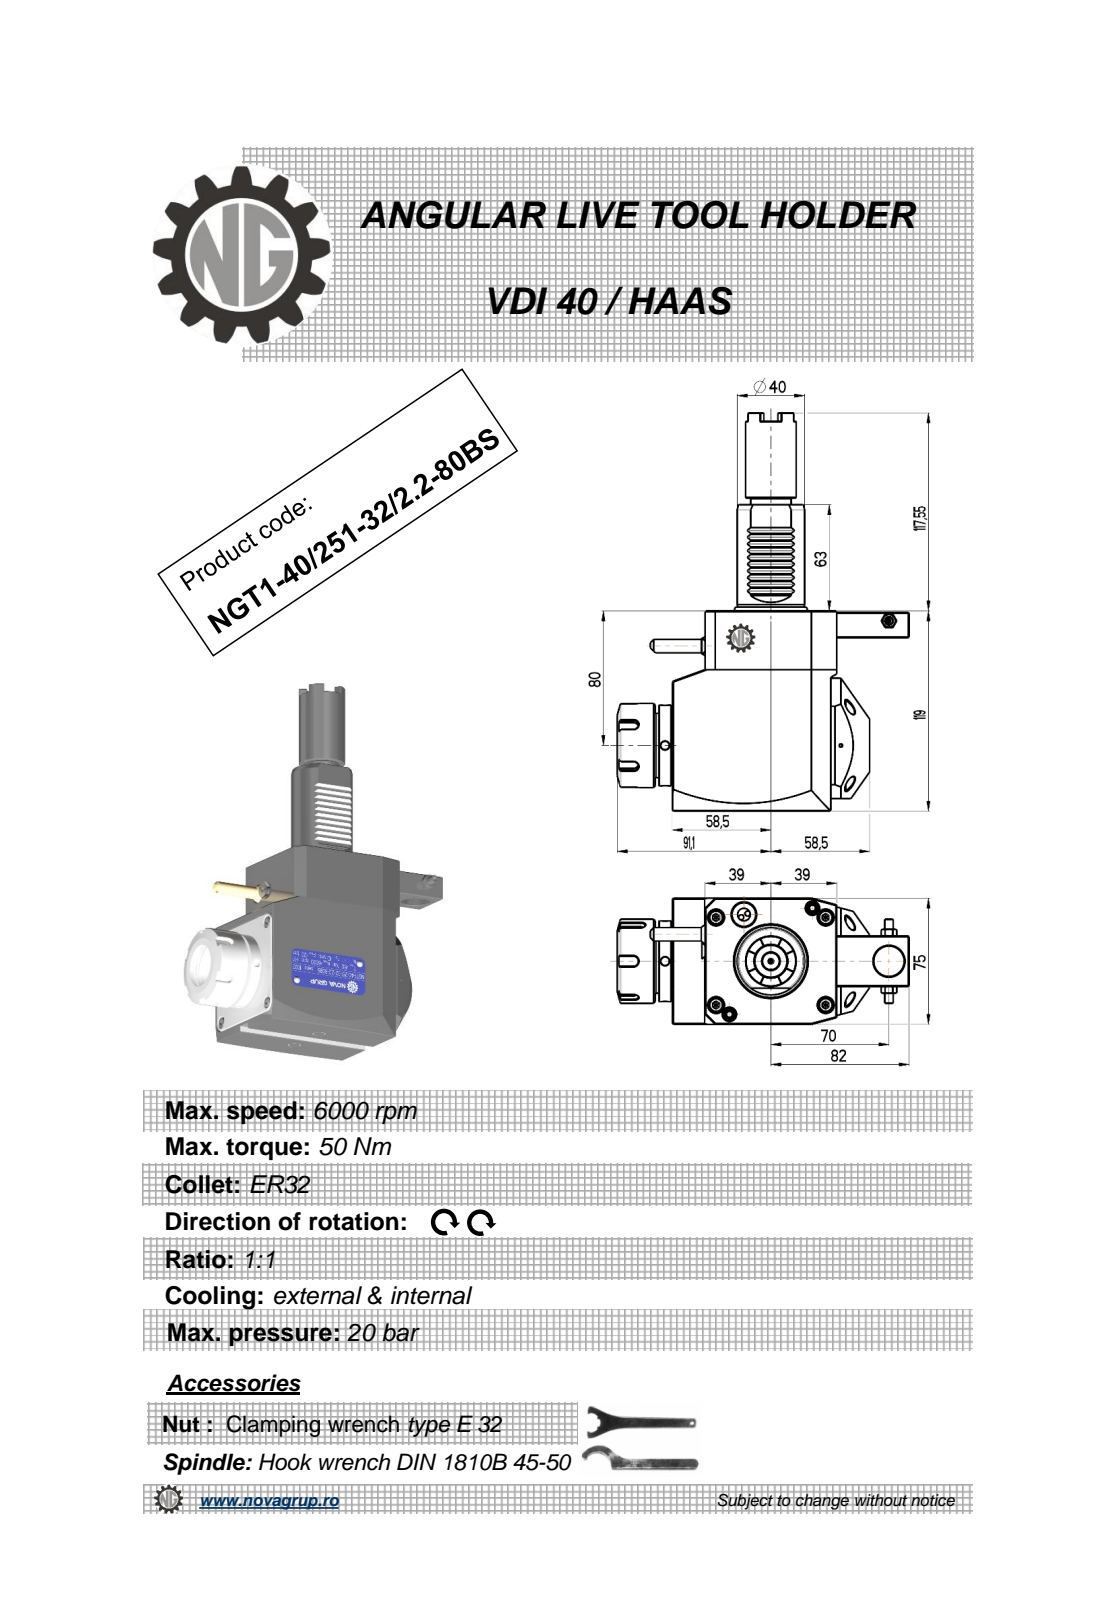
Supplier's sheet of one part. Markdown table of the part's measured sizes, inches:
| quantity | value |
| --- | --- |
| part name | NGT1_40_251_32_2_2_80BS |
| STEP written by | PRO/ENGINEER BY PARAMETRIC TECHNOLOGY CORPORATION, 2010280 (CONFIG_CONTROL_DESIGN) |
| units | inches |
| bodies | 1 solid, 475 faces (236 planar, 100 cylindrical, 139 other) |
| overall size | 9.313 × 6.815 × 3.016 |
| volume | 62.85 in³ |
| surface area | 128.9 in² |
| round holes (diameter × count) | 0.197 × 3, 0.118 × 1, 0.165 × 1, 0.374 × 1, 0.709 × 1, 1.063 × 1 |
| round bosses / shafts (diameter × count) | 1.969 × 1, 1.89 × 1, 1.634 × 1, 1.614 × 1, 1.575 × 1, 1.181 × 1, 0.945 × 1, 0.394 × 1 |
| partial cylindrical surfaces (radius × count) | 0.01 × 12, 0.012 × 10, 0.008 × 6, 0.118 × 5, 0.228 × 2, 0.236 × 2, 23.622 × 2, 0.02 × 1 |
| main face-to-face distances | 2.953, 4.685, 0.768, 3.839, 3.071, 0.039, 0.138, 0.886, 0.76, 3.831 |
| hole center spacings | 0.824, 2.407, 2.854, 5.226, 5.983 |
